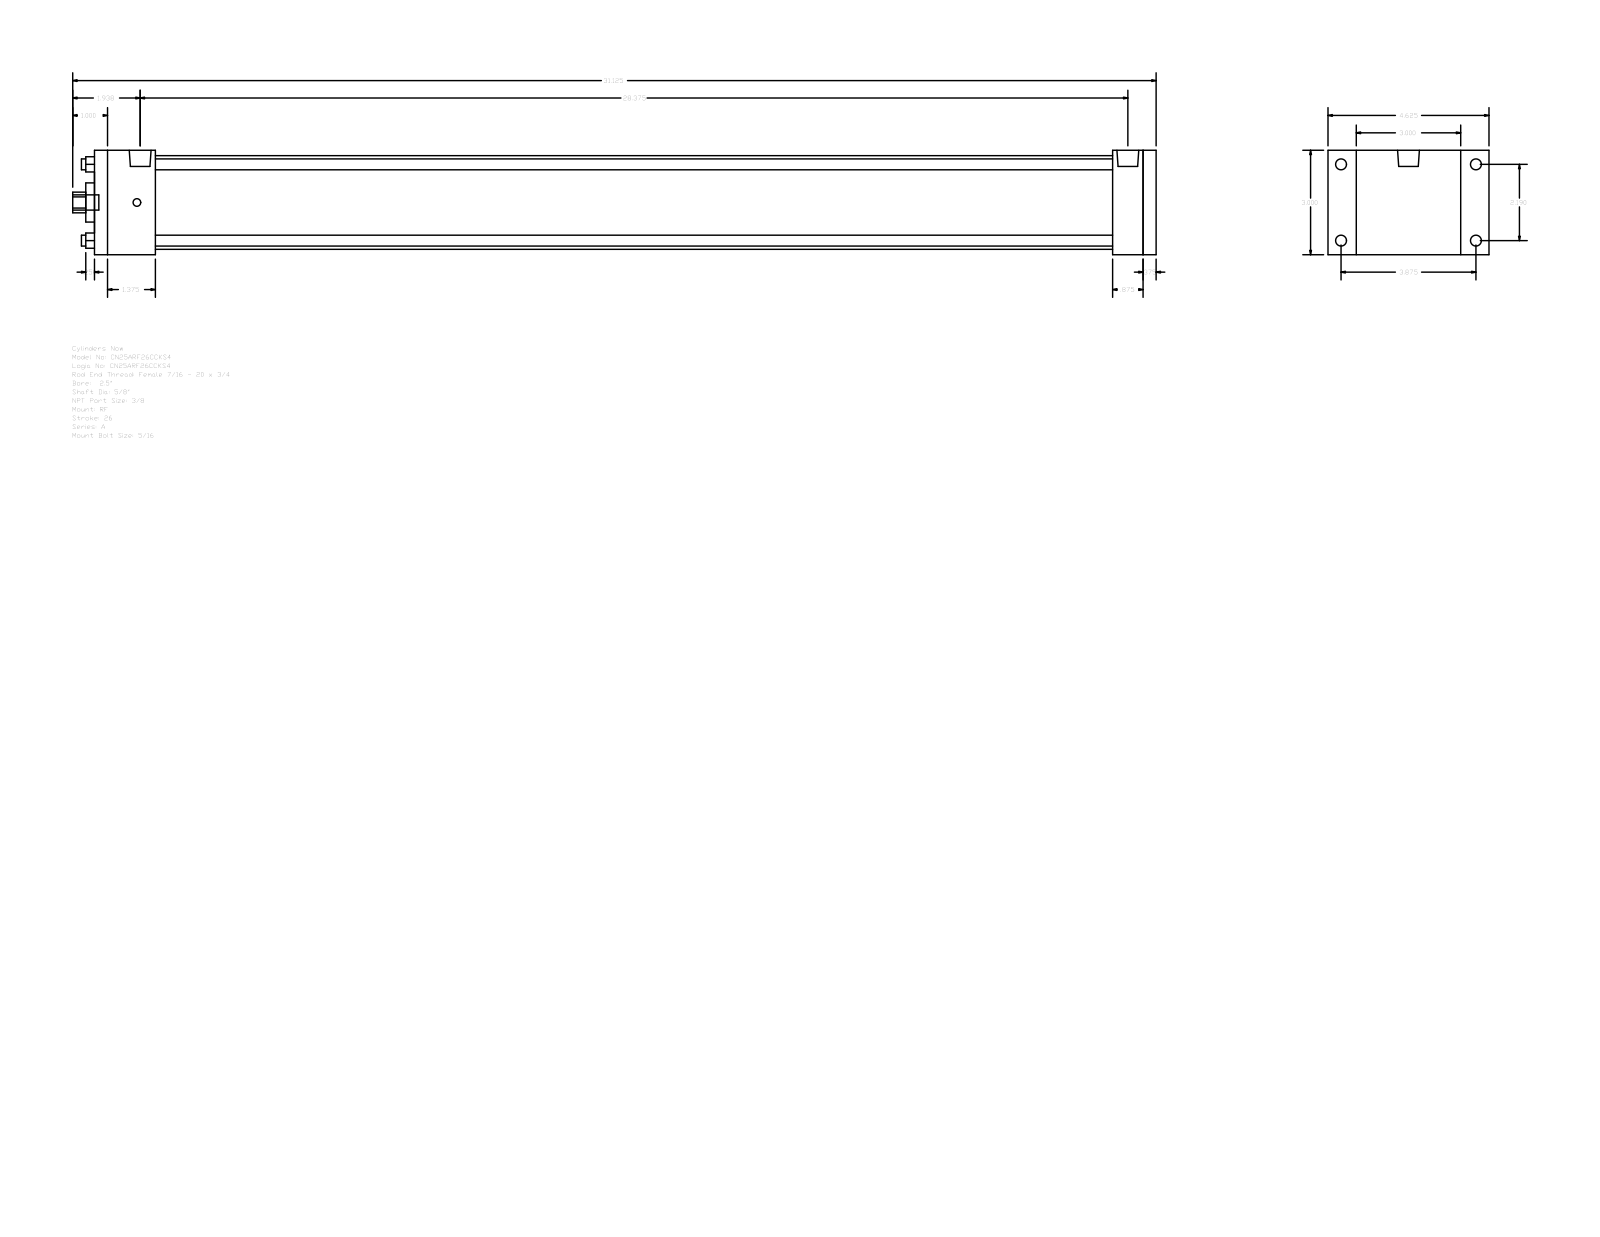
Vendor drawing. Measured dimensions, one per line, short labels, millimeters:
name: A_RF__0250_0.625
written by: GSSL Pune (CONFIG_CONTROL_DESIGN)
unit: mm
bodies: 0 solids, 92 faces (64 planar, 28 cylindrical, 0 other)
size: 790.58 × 117.47 × 76.2
holes: 4× ⌀7.94, 1× ⌀15.88, 1× ⌀28.57, 1× ⌀68.33
bosses: 4× ⌀7.94, 4× ⌀5.56, 2× ⌀15.93, 1× ⌀11.11
rounds: 1× R7.54
face distances: 76.2, 774.7, 9.53, 765.17, 44.45, 31.75, 742.95, 698.5, 720.72, 730.25
hole spacings: 39.33, 55.62, 78.66
